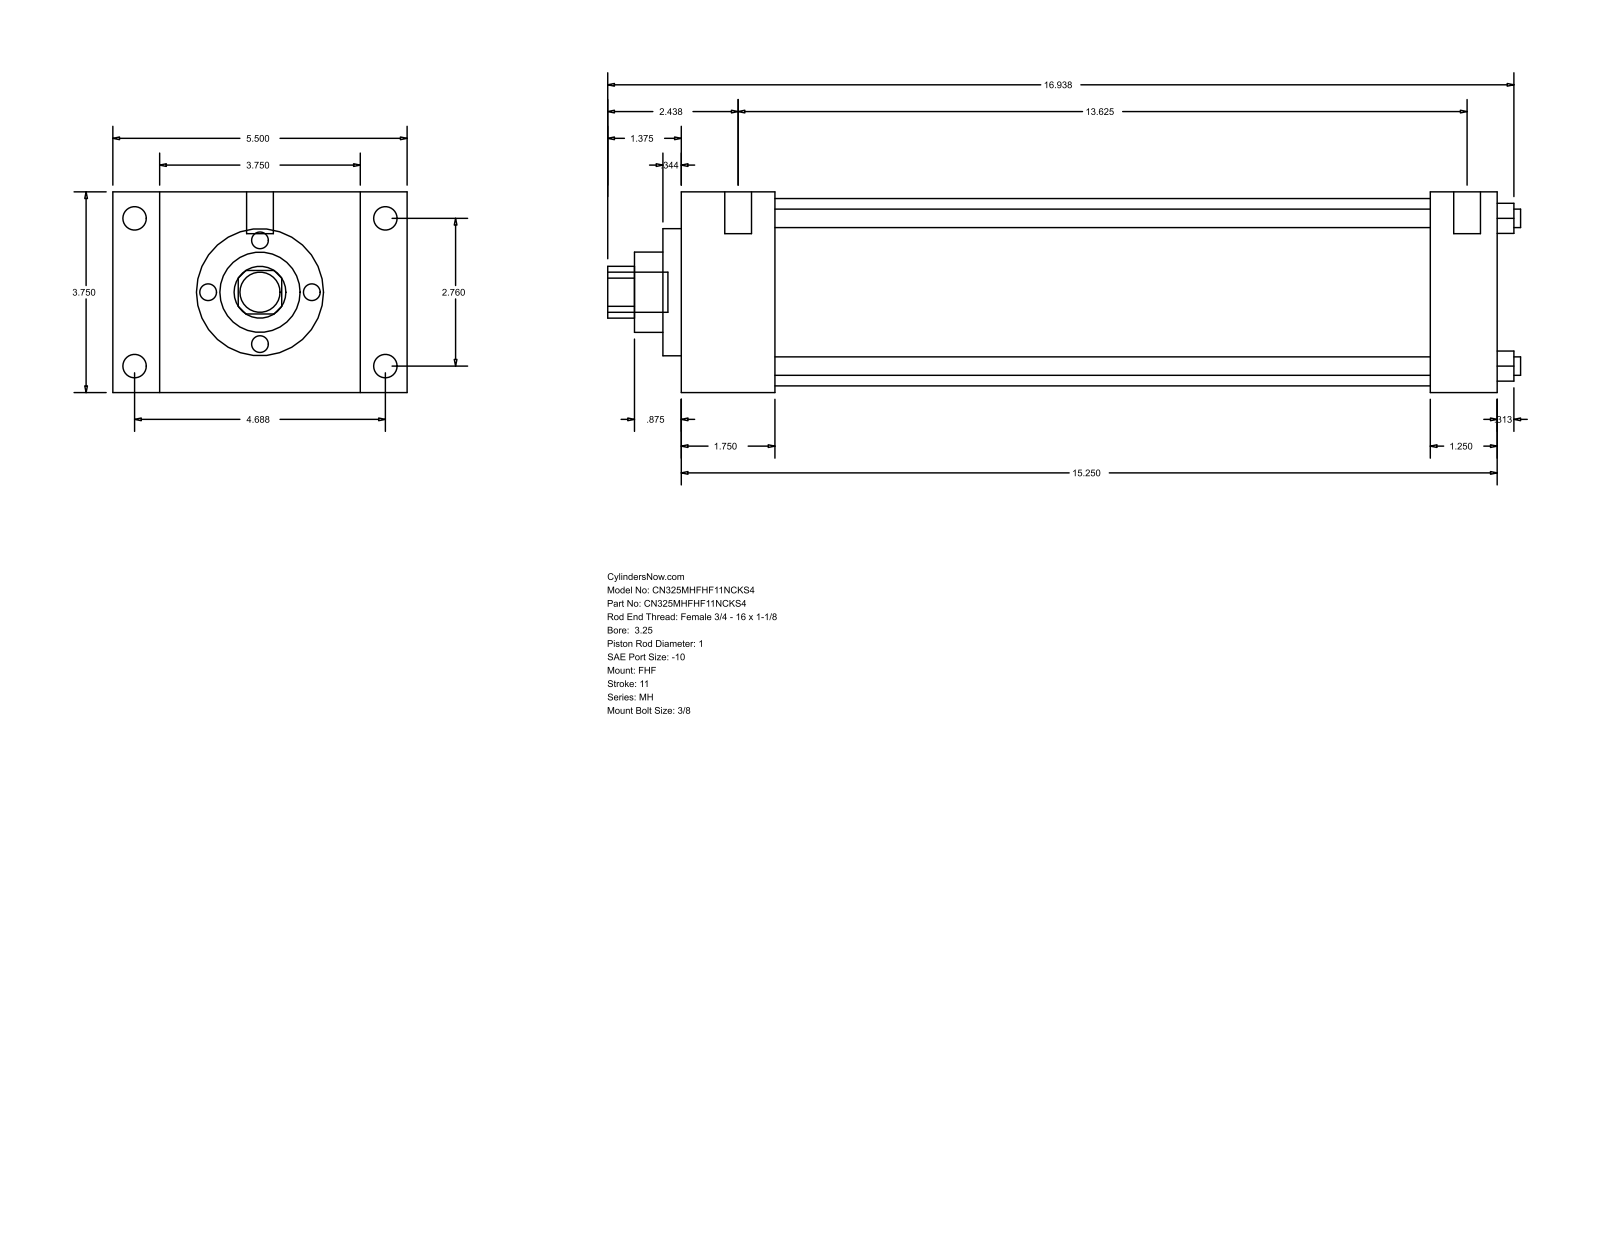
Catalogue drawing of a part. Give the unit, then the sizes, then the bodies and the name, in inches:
Units: inches
Overall size (bounding box): 17.063 × 5.5 × 3.75
Round holes (diameter × count): ⌀0.345 ×4, ⌀1 ×1, ⌀1.5 ×1, ⌀2.375 ×1, ⌀3.5 ×1
Round bosses / shafts (diameter × count): ⌀0.438 ×4, ⌀0.219 ×4, ⌀0.5 ×2, ⌀0.75 ×1
Partial cylindrical surfaces — rounded edges, fillets, slot ends (radius × count): R0.484 ×1
Main face-to-face distances: 3.75, 15.25, 1.75, 13.5, 0.875, 4.625, 5.5, 14, 12.25, 1.25
Hole centre spacings: 1.952, 2.76, 3.903
Bodies: 0 solids, 90 faces (61 planar, 29 cylindrical, 0 other)
Part name (STEP PRODUCT): MH_FHF__0325_1
STEP written by: GSSL Pune (CONFIG_CONTROL_DESIGN)
